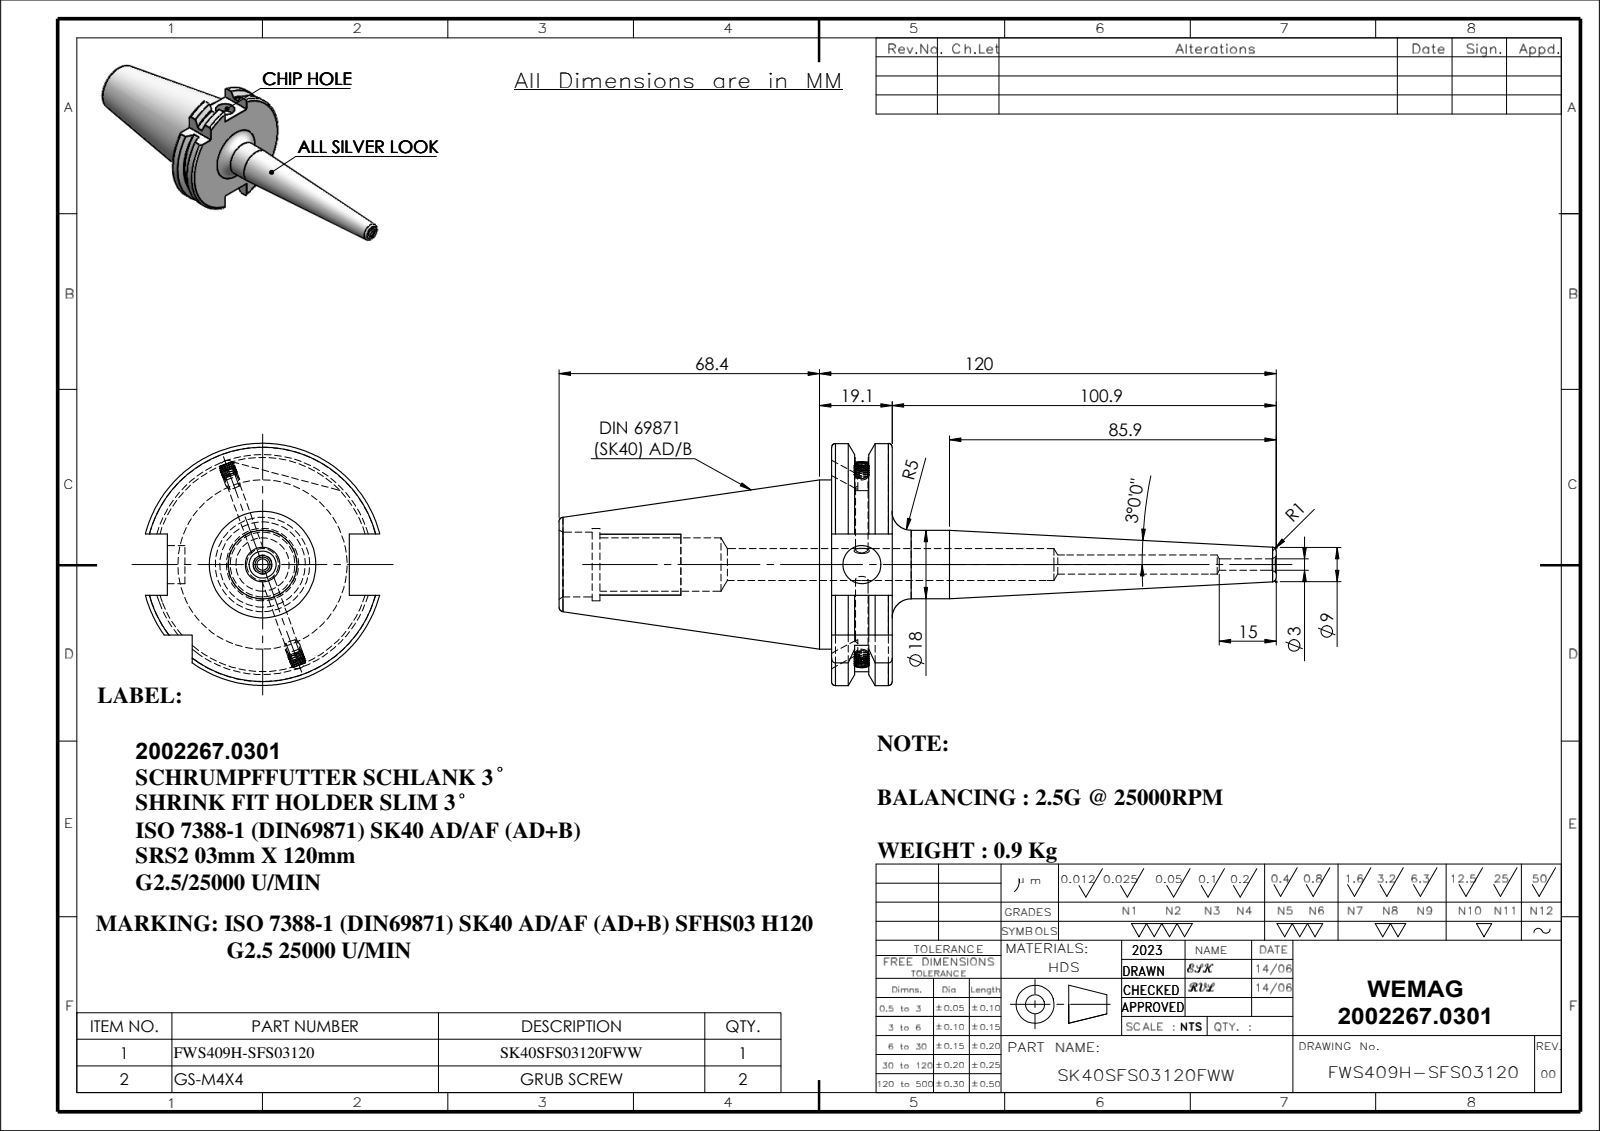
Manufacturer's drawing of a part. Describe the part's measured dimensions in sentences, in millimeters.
The part is named "SK40SFS03120FWW; 91406-SRS03120; GS-M4X4_DIN 913 - M4 x 4-N". Its 3-D file was written by "SolidWorks 2018 (CONFIG_CONTROL_DESIGN)". It is 3 solids with 198 faces: 46 planar, 54 cylindrical and 98 other. Overall it measures 188.4 by 63.55 by 61.48 millimeters. Its volume is 116 257 cubic millimeters and its surface area 27 098 square millimeters. Round holes: 1 of diameter 3, 1 of diameter 3.3, 1 of diameter 5, 1 of diameter 8.4, 1 of diameter 10, 1 of diameter 14, 1 of diameter 17, 1 of diameter 19. Round bosses or shafts: 2 of diameter 4, 1 of diameter 44.45, 1 of diameter 18. Partial cylindrical surfaces (rounded edges, fillets, slot ends): 1 of radius 28.12, 1 of radius 31.77. The main face-to-face distances are 15.9, 16.1, 47.8, 71.6, 87.5, 10.7, 60.9, 76.8, 77.62, 66.92.
